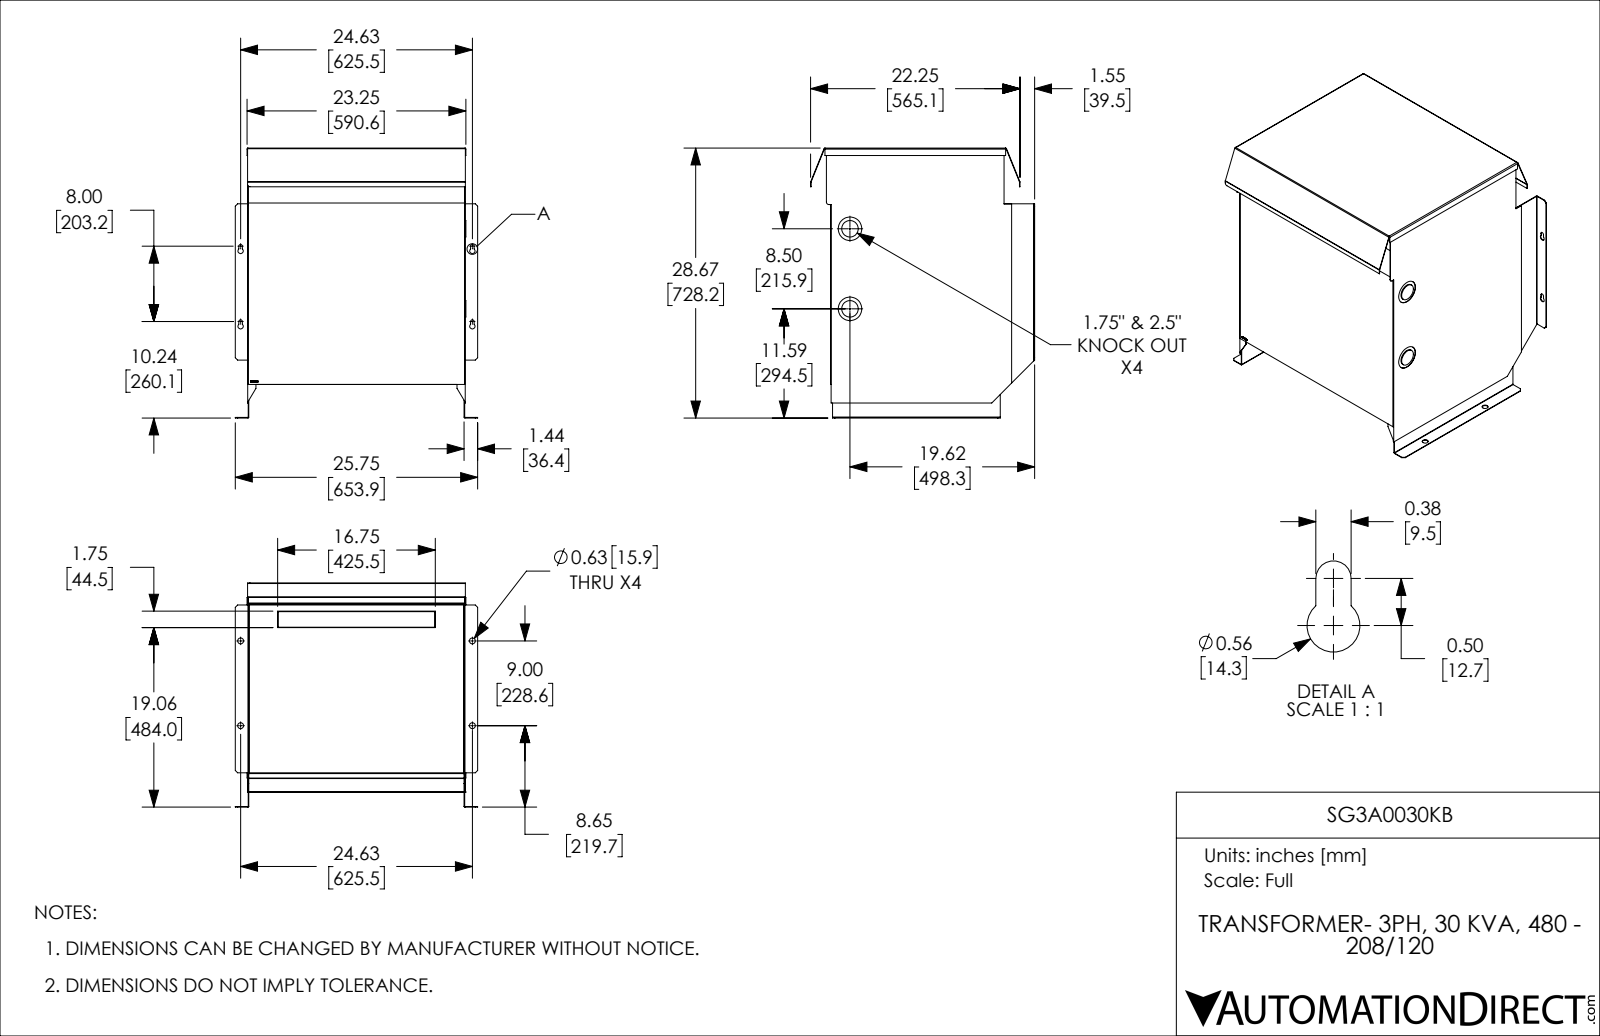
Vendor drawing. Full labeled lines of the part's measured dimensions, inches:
Part name (STEP PRODUCT): SG3A0030KB
STEP written by: SolidWorks 2018 (AUTOMOTIVE_DESIGN)
Units: inches
Bodies: 7 solids, 332 faces (217 planar, 81 cylindrical, 34 other)
Overall size (bounding box): 28.668 × 25.745 × 23.801
Volume: 205.5 in³ · Surface area: 7 302 in²
Round holes (diameter × count): ⌀0.625 ×4, ⌀2.5 ×2
Round bosses / shafts (diameter × count): ⌀1.75 ×2
Partial cylindrical surfaces — rounded edges, fillets, slot ends (radius × count): R0.03 ×12, R0.09 ×12, R0.06 ×6, R0.11 ×6, R0.188 ×4, R0.281 ×4, R0.25 ×3
Main face-to-face distances: 0.06, 0.05, 23.055, 22.995, 23.115, 17.996, 18.046, 18.056, 18.106, 25.058
Hole centre spacings: 9, 24.625, 26.218, 8.5
